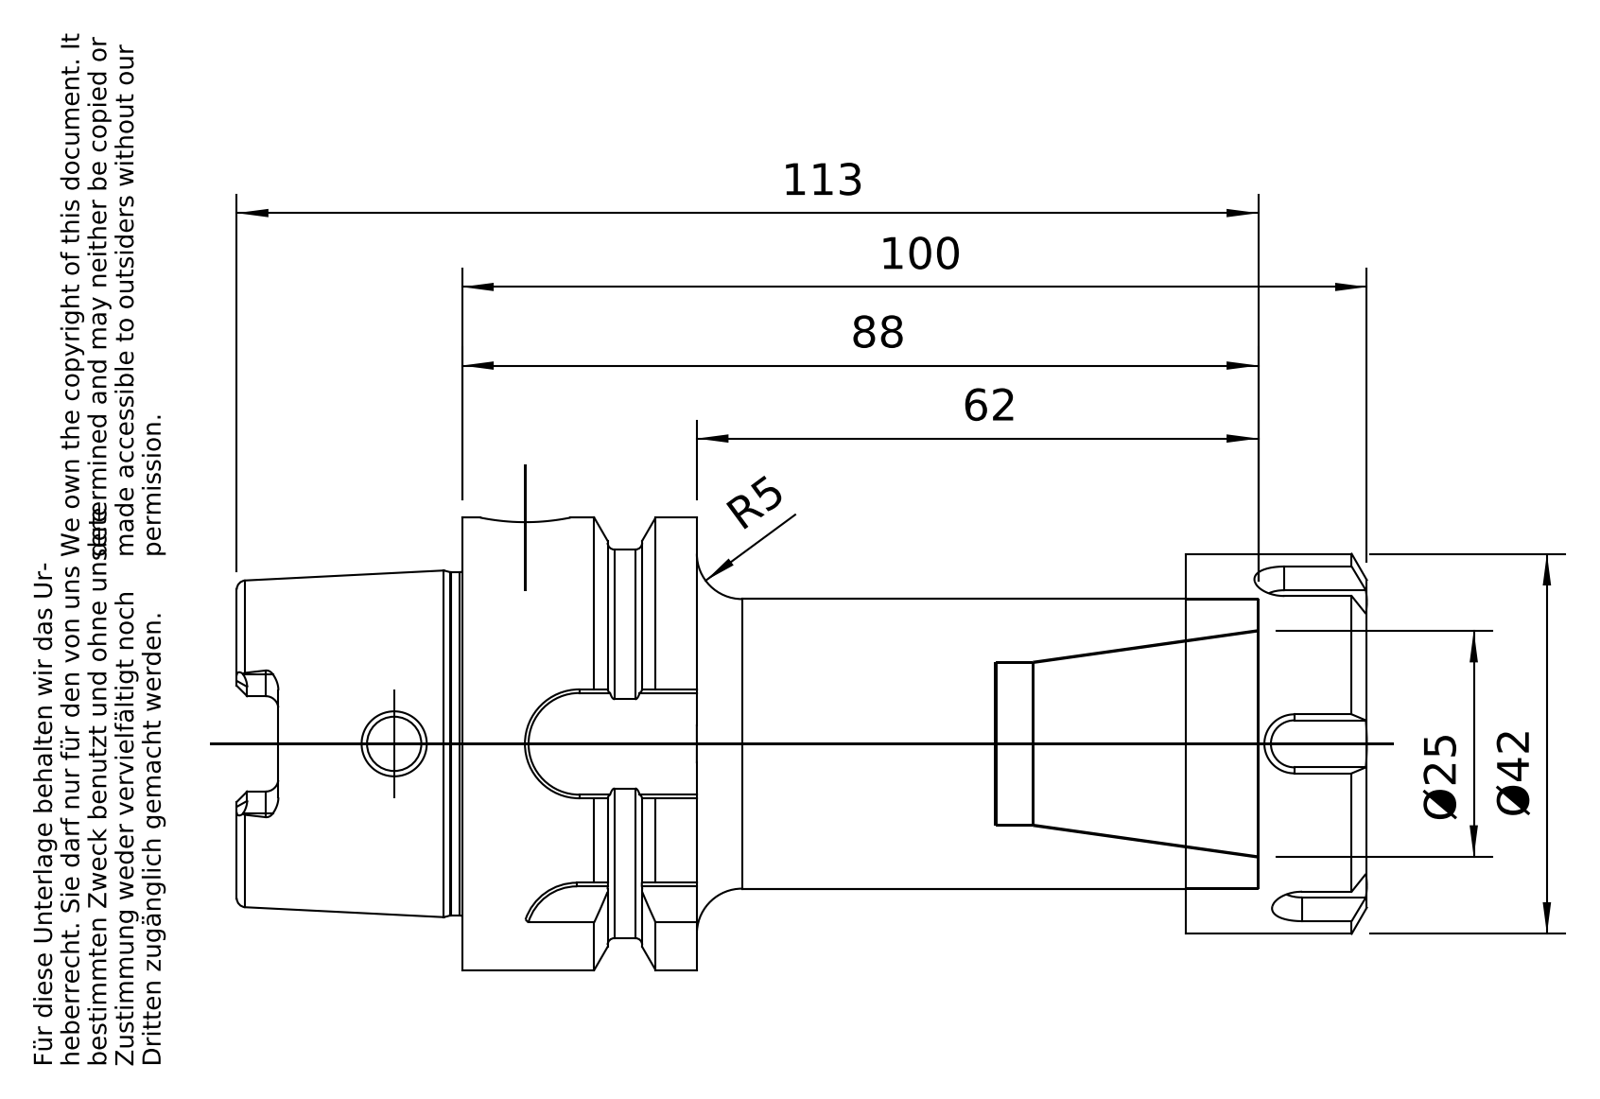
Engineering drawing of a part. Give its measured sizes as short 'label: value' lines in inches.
name: A50-020-25; 83-912-25; A50-020-25_ASM
written by: PRO/ENGINEER BY PARAMETRIC TECHNOLOGY CORPORATION, 2010430 (CONFIG_CONTROL_DESIGN)
unit: in
bodies: 2 solids, 227 faces (84 planar, 51 cylindrical, 92 other)
size: 4.917 × 1.969 × 1.969
volume: 7.009 in³; area: 43.7 in²
holes: 1× ⌀0.236, 1× ⌀0.394, 1× ⌀0.551, 1× ⌀0.63, 1× ⌀0.643, 1× ⌀0.65, 1× ⌀0.709, 1× ⌀1.025, 1× ⌀1.263
bosses: 1× ⌀1.969, 1× ⌀1.691, 1× ⌀1.654, 1× ⌀1.493, 1× ⌀1.26
rounds: 6× R0.055, 4× R0.094, 3× R0.236, 1× R0.237
face distances: 0.787, 3.15, 3.937, 1.022, 2.128, 2.915, 3.465, 2.443, 0.315, 0.472
